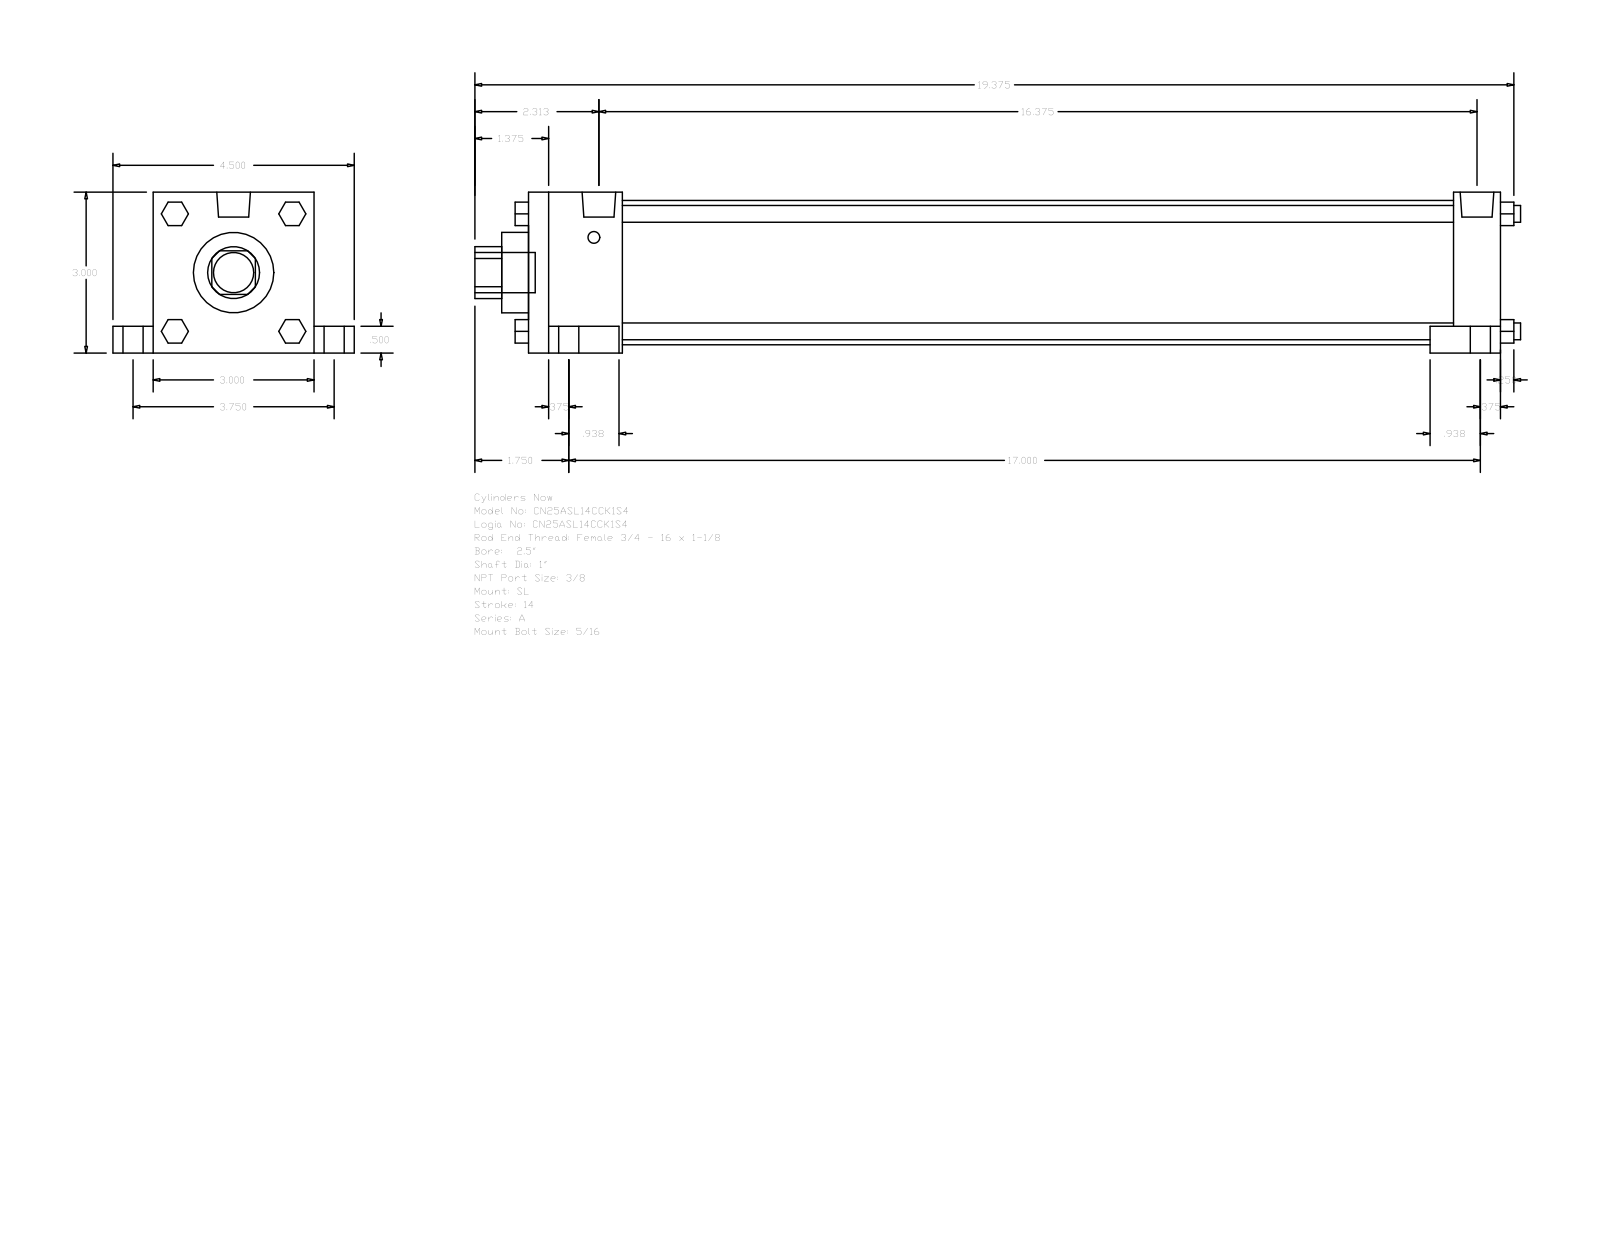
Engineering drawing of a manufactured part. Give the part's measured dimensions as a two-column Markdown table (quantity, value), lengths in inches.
| quantity | value |
| --- | --- |
| part name | A_SL__0250_1 |
| STEP written by | GSSL Pune (CONFIG_CONTROL_DESIGN) |
| units | inches |
| bodies | 0 solids, 148 faces (112 planar, 36 cylindrical, 0 other) |
| overall size | 19.5 × 4.5 × 3 |
| round holes (diameter × count) | 1 × 1, 1.5 × 1, 2.69 × 1 |
| round bosses / shafts (diameter × count) | 0.625 × 4, 0.375 × 4, 0.313 × 4, 0.219 × 4, 0.627 × 2, 0.75 × 1 |
| partial cylindrical surfaces (radius × count) | 0.484 × 1 |
| main face-to-face distances | 3, 18.125, 0.5, 0.875, 1.75, 16.375, 17.25, 15.5, 0.75, 2.5 |
